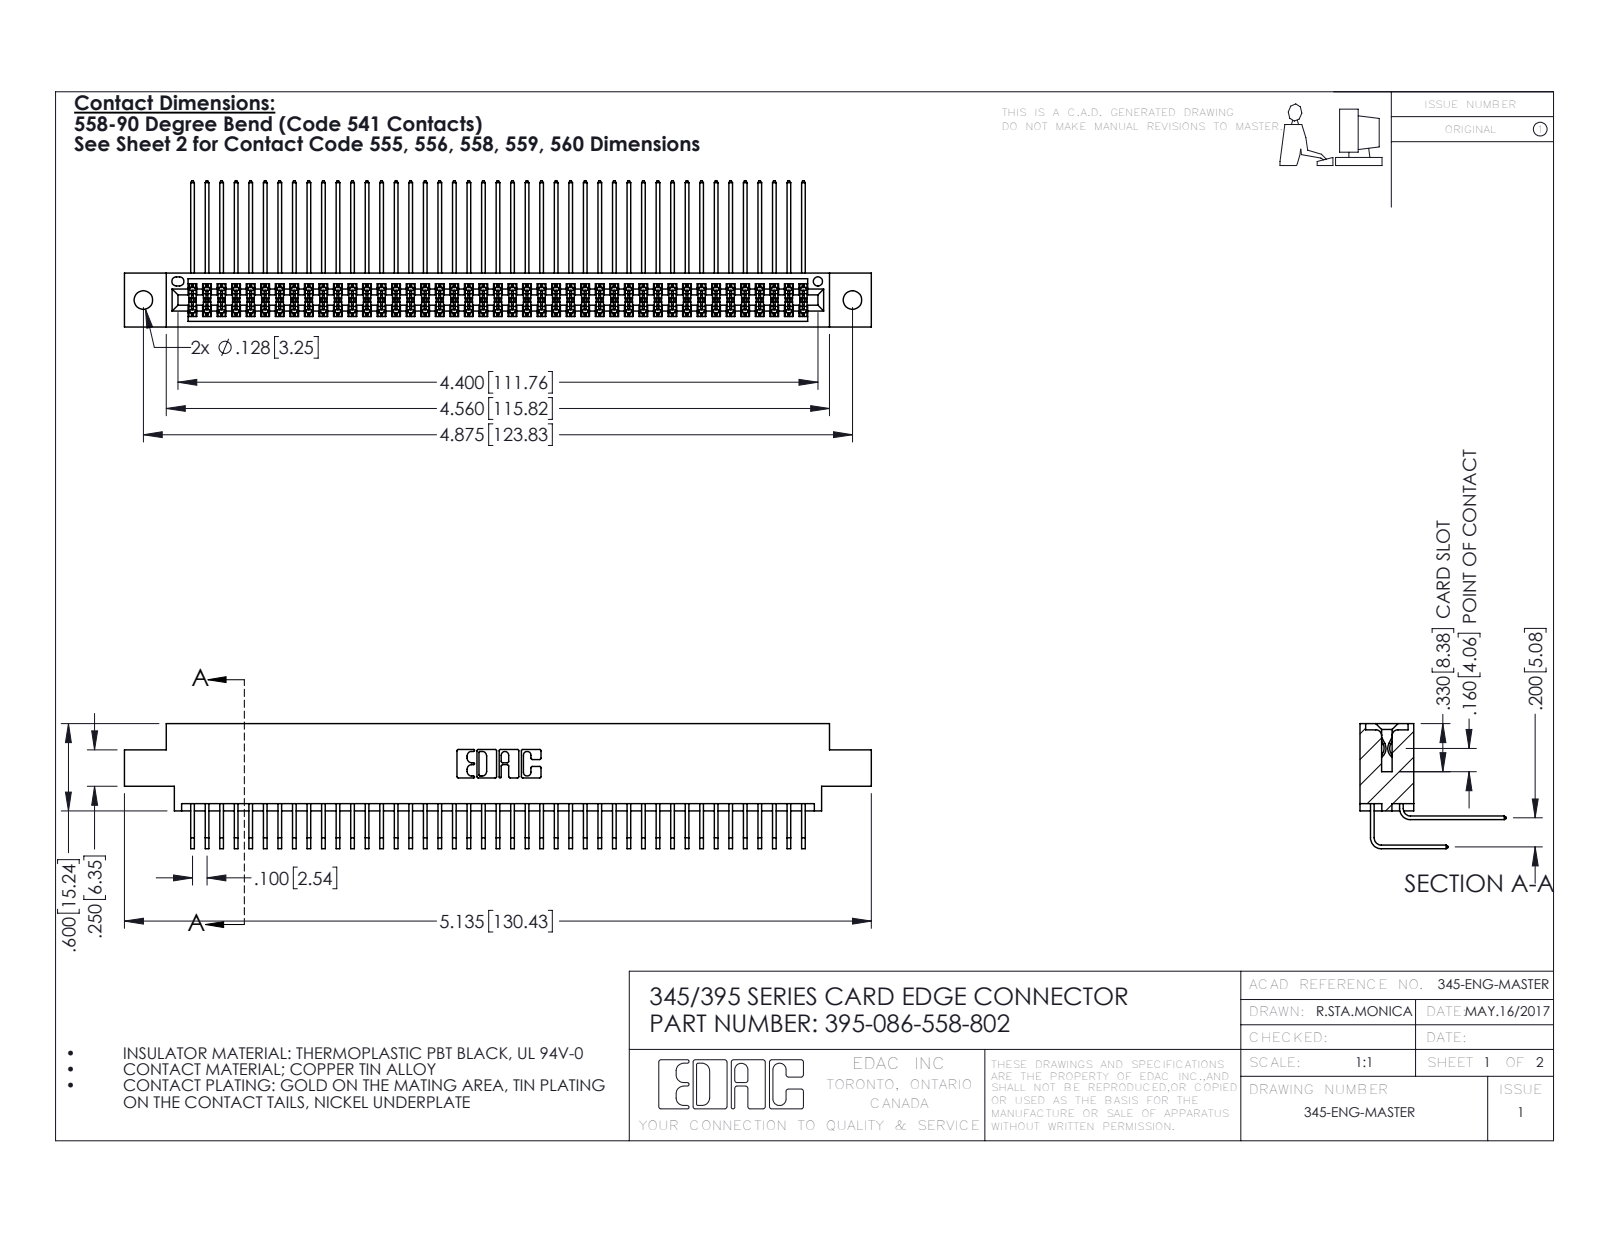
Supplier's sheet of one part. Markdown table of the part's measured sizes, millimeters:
| quantity | value |
| --- | --- |
| part name | 345 Part_0.170 Offset - 0.128 Dia; 345-292-001_558 559 Tail - 1; 345-292-001_558 Tail - 2; 395-086-558-802 |
| STEP written by | SolidWorks 2016 (CONFIG_CONTROL_DESIGN) |
| units | millimeters |
| bodies | 87 solids, 4602 faces (3094 planar, 1508 cylindrical, 0 other) |
| overall size | 130.4 × 25.5 × 21.8 |
| volume | 13 000 mm³ |
| surface area | 21 480 mm² |
| round holes (diameter × count) | 3.3 × 2, 1.6 × 1 |
| partial cylindrical surfaces (radius × count) | 0.2 × 129, 0.3 × 22, 0.2 × 6, 0.8 × 6, 0.7 × 3, 0.4 × 2, 0.5 × 2, 0.6 × 2 |
| main face-to-face distances | 1.8, 7.6, 5.1, 9.4, 2.5, 6.9, 0.6, 5.7, 4.4, 0.6 |
| hole center spacings | 6.9, 117.8, 123.8 |
